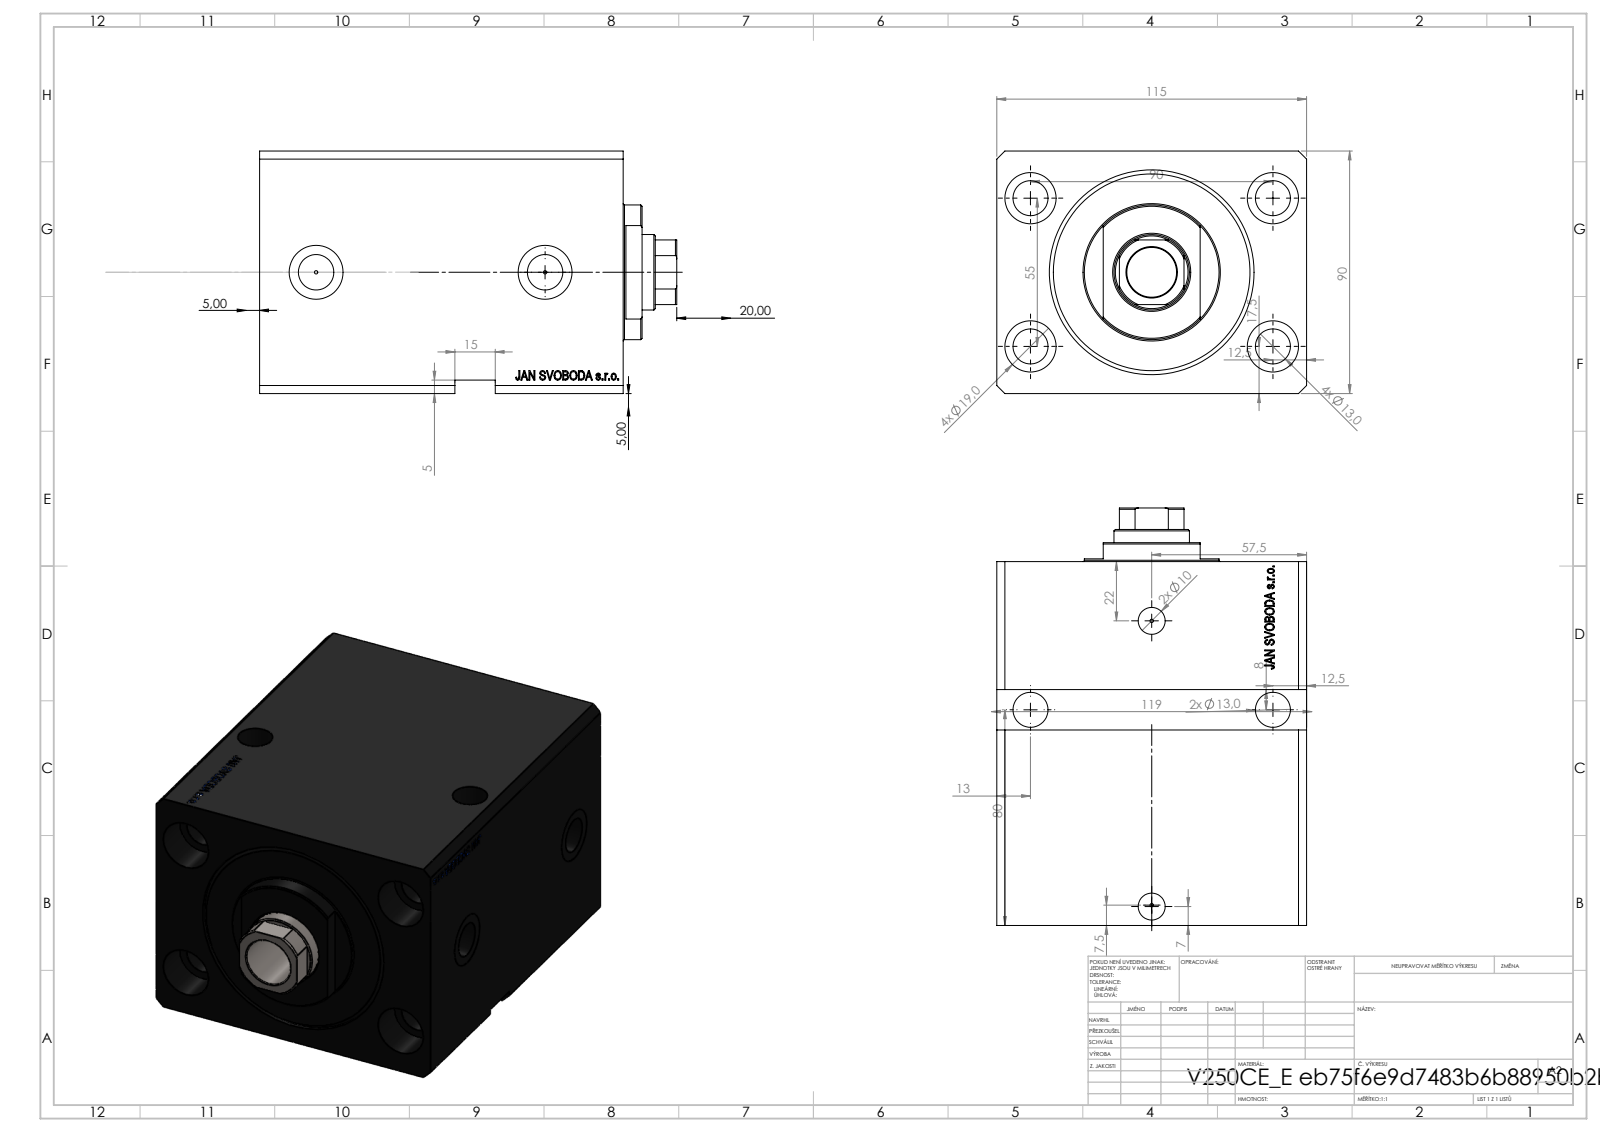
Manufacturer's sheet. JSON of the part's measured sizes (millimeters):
{"part_name": "V250CE_E_Body; V250CE_C_VCP; V250CE_VC_E", "step_written_by": "SolidWorks 2019 (CONFIG_CONTROL_DESIGN)", "units": "millimeters", "bodies": {"solids": 3, "faces": 973, "planar": 471, "cylindrical": 116, "other": 386}, "overall_size": [155, 115, 90], "volume_mm3": 1140000, "surface_area_mm2": 175067, "round_holes": [[13, 8], [1.25, 4], [19, 4], [10, 2], [13.16, 2], [20, 2], [18.5, 1], [28, 1], [63, 1], [76, 1]], "round_bosses_or_shafts": [[50, 1]], "partial_cylinders_radius": [[13.5, 1]], "face_to_face_distances": [115, 90, 135, 17.9, 117.1, 20, 97.1, 65, 47.1, 50], "hole_center_spacings": [52.74, 55.8, 85.76, 90, 40, 55, 55.49, 85.3]}
